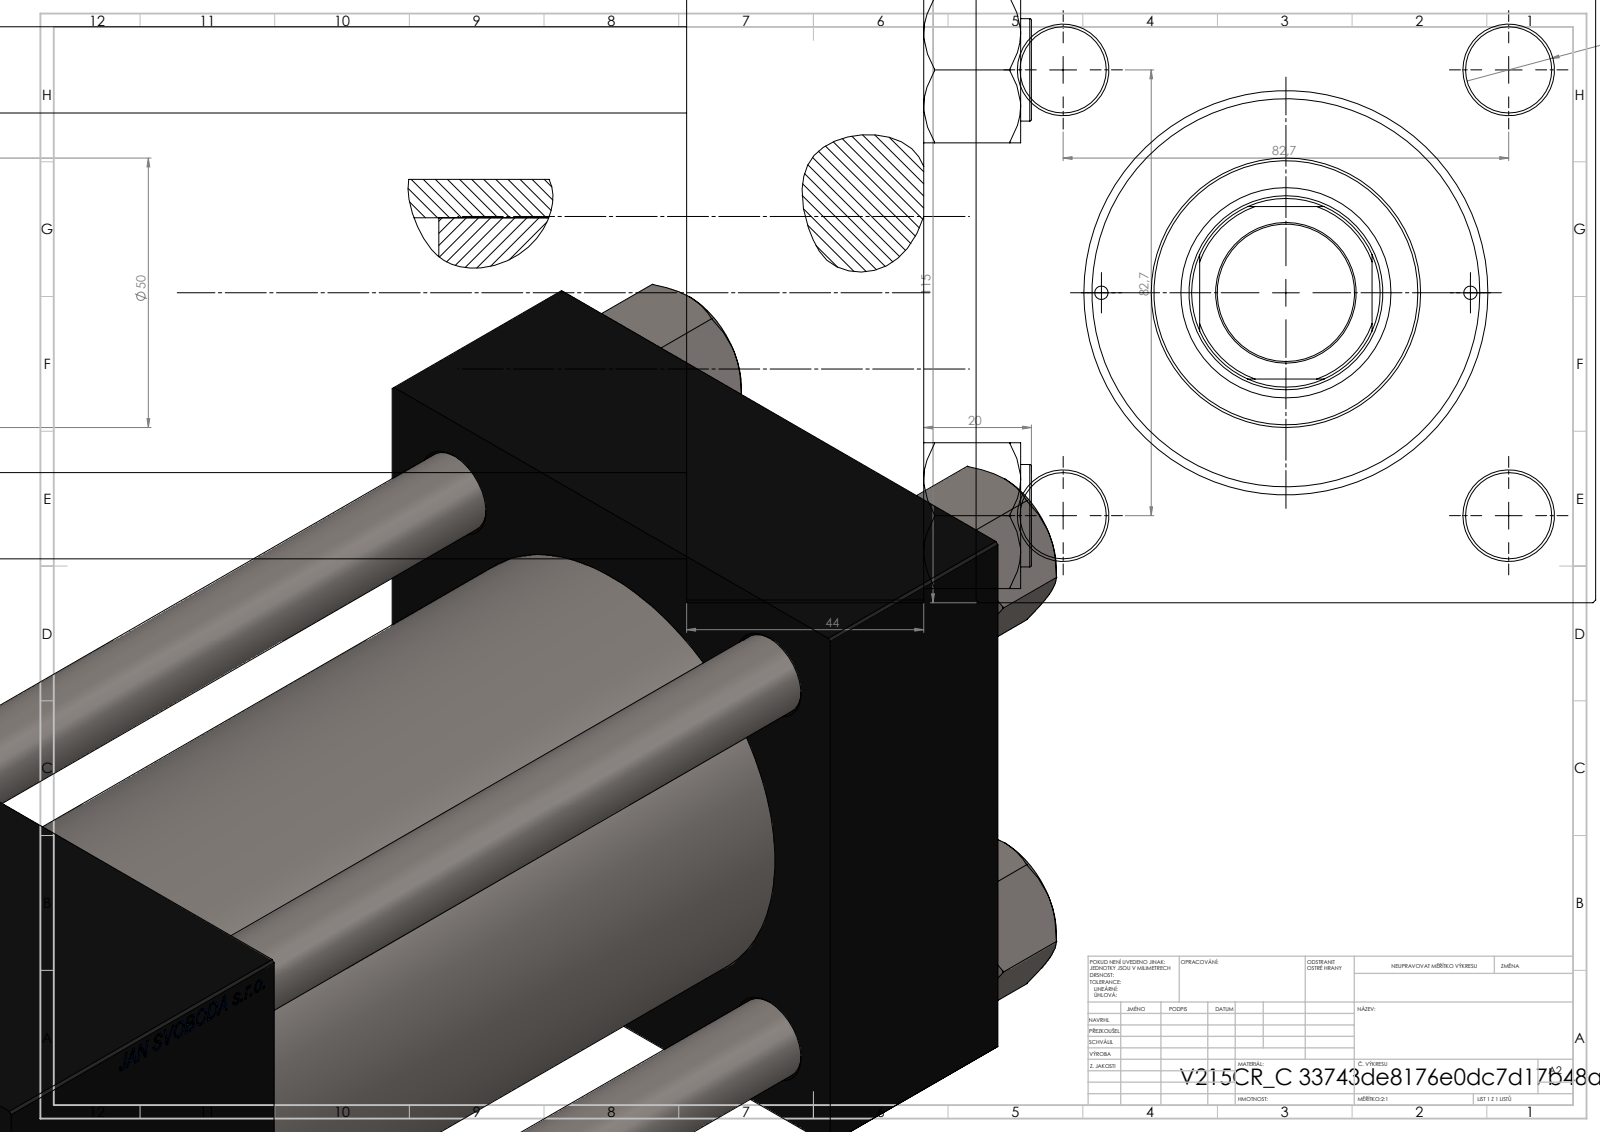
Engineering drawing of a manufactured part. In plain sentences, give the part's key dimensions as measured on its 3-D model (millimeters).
The part is named "V215CR_C_Body; V215CR_C_TYCINKA; NUT_M5_C; V215CR_VCP_C (+1 more)". Its 3-D file was written by "SolidWorks 2019 (CONFIG_CONTROL_DESIGN)". It is 11 solids with 1202 faces: 576 planar, 90 cylindrical and 536 other. Overall it measures 310 by 115 by 115 millimeters. Its volume is 1 995 000 cubic millimeters and its surface area 335 365 square millimeters. Round holes: 4 of diameter 16, 2 of diameter 2.5, 2 of diameter 7, 2 of diameter 26.44, 2 of diameter 35, 1 of diameter 25.5, 1 of diameter 36, 1 of diameter 39, 1 of diameter 61, 1 of diameter 72, 1 of diameter 80. Round bosses or shafts: 4 of diameter 19, 1 of diameter 86, 1 of diameter 50. Partial cylindrical surfaces (rounded edges, fillets, slot ends): 1 of radius 17.5. The main face-to-face distances are 115, 44, 259, 215, 190, 146, 69, 100, 230.3, 186.3. The hole center spacings are 41.96, 58.48, 82.7, 86.17, 34.25, 116.96, 68.5, 191.
